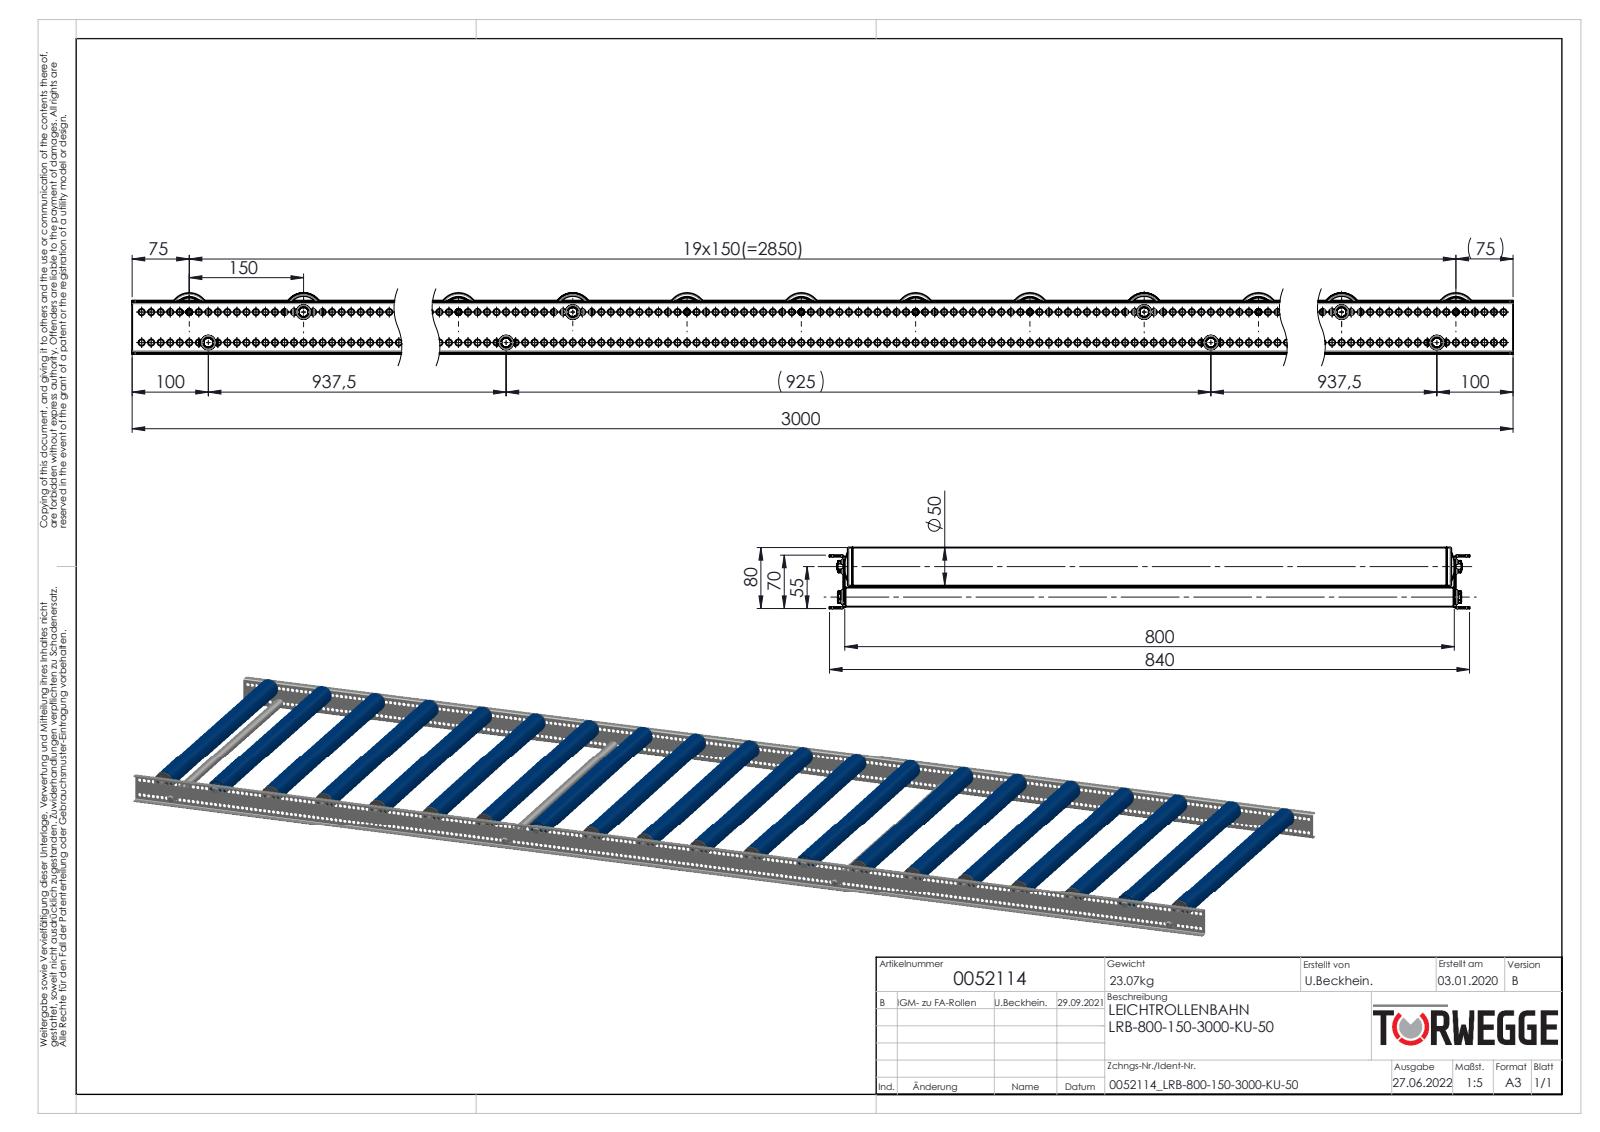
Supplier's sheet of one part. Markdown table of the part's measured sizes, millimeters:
| quantity | value |
| --- | --- |
| part name | Profil_LRB-20x70x20x2_KFG_S109080_U-PROFIL-20-70-20-2-LRB-L=3000; 0024178_Passscheibe_DIN988_12x18x1; Traversen_KFG_L800; KUT100-50x2,8-KB-A8-FA_KFG_0054463_KUT100-50x2,8-KB-A8-FA-EL=800 (+8 more) |
| STEP written by | SolidWorks 2020 (AUTOMOTIVE_DESIGN) |
| units | millimeters |
| bodies | 414 solids, 8500 faces (2012 planar, 3960 cylindrical, 2528 other) |
| overall size | 3000 × 840 × 80 |
| volume | 10 210 000 mm³ |
| surface area | 7 627 000 mm² |
| round holes (diameter × count) | 8.2 × 478, 7.6 × 16, 8 × 16, 25 × 16, 30 × 16, 35 × 16, 39.4 × 16, 40 × 16, 6.8 × 8, 12 × 4, 12.1 × 4, 16 × 4 |
| round bosses / shafts (diameter × count) | 50 × 20, 44.4 × 16, 38 × 16, 36 × 16, 33 × 16, 22 × 16, 21 × 16, 25 × 8 |
| partial cylindrical surfaces (radius × count) | 0.6 × 32, 0.75 × 32, 2.45 × 32, 2.5 × 16, 4.87 × 16, 7 × 16, 4 × 8, 2 × 4 |
| main face-to-face distances | 2, 802, 68, 800, 804, 70, 66, 6, 792, 12 |
| hole center spacings | 12.5, 25, 37.5, 50, 62.5, 75, 87.5, 100 |
